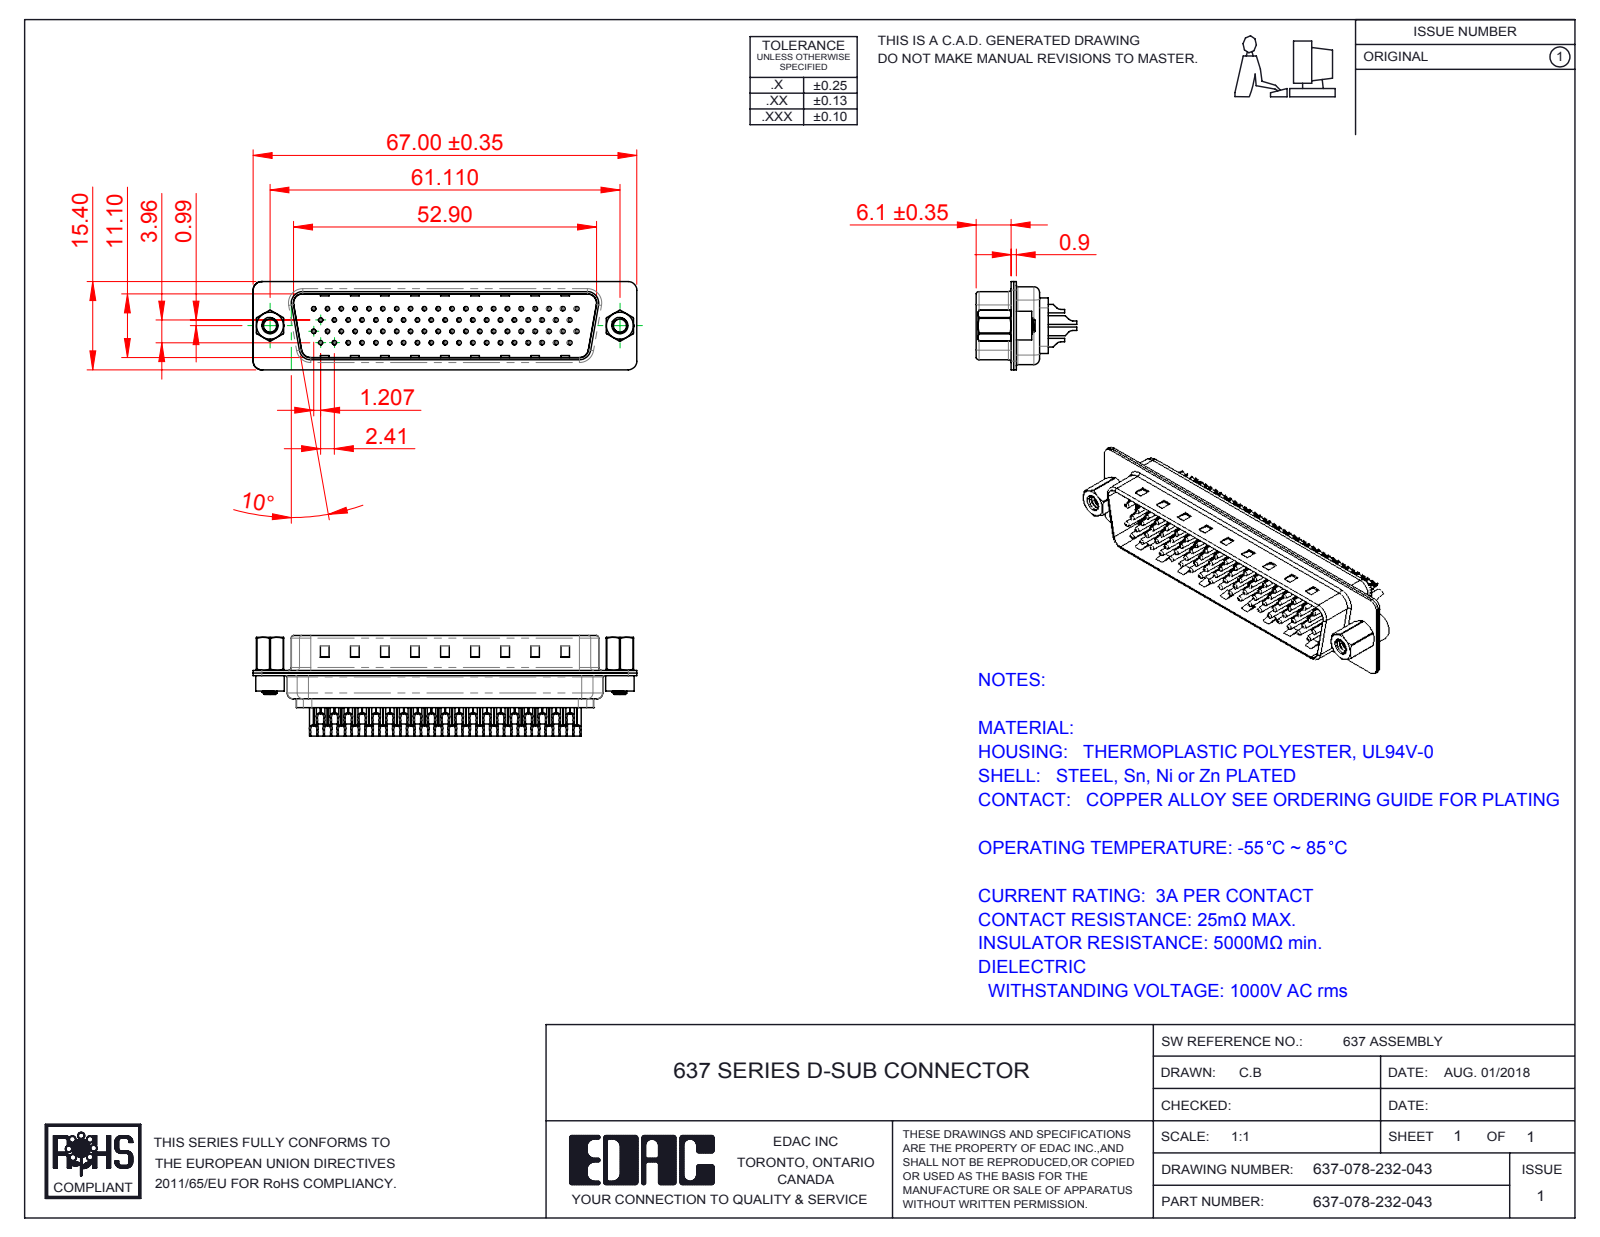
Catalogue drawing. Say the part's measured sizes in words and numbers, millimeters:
The part is named "637 Contact Row 2_32(78); 637 4-40 Hex Standoff; 637 Contact Row 1_32(78); 637 Shell Rear_78 Contacts (+6 more)". Its 3-D file was written by "SolidWorks 2016 (CONFIG_CONTROL_DESIGN)". It is 85 solids with 5530 faces: 1317 planar, 2475 cylindrical and 1738 other. Overall it measures 67 by 17.55 by 15.4 millimeters. Its volume is 4 647 cubic millimeters and its surface area 17 263 square millimeters. Round holes: 150 of diameter 1.6, 78 of diameter 0.35, 78 of diameter 1.1, 72 of diameter 0.75, 72 of diameter 2, 3 of diameter 4, 2 of diameter 2.26, 2 of diameter 2.29, 2 of diameter 4.8. Round bosses or shafts: 78 of diameter 2, 78 of diameter 1.5, 78 of diameter 0.75, 2 of diameter 5, 2 of diameter 4.9, 2 of diameter 2.79, 1 of diameter 4.8. Partial cylindrical surfaces (rounded edges, fillets, slot ends): 16 of radius 1.5, 12 of radius 2, 8 of radius 0.5, 8 of radius 1, 4 of radius 0.25, 4 of radius 0.55, 4 of radius 0.7, 4 of radius 0.95. The main face-to-face distances are 0.45, 0.4, 1.5, 1.95, 11.9, 11.5, 0.7, 11.1, 0.9, 0.8. The hole center spacings are 2.41, 7.24, 6.06, 9.65, 6.96, 8.46, 14.54, 16.89.
